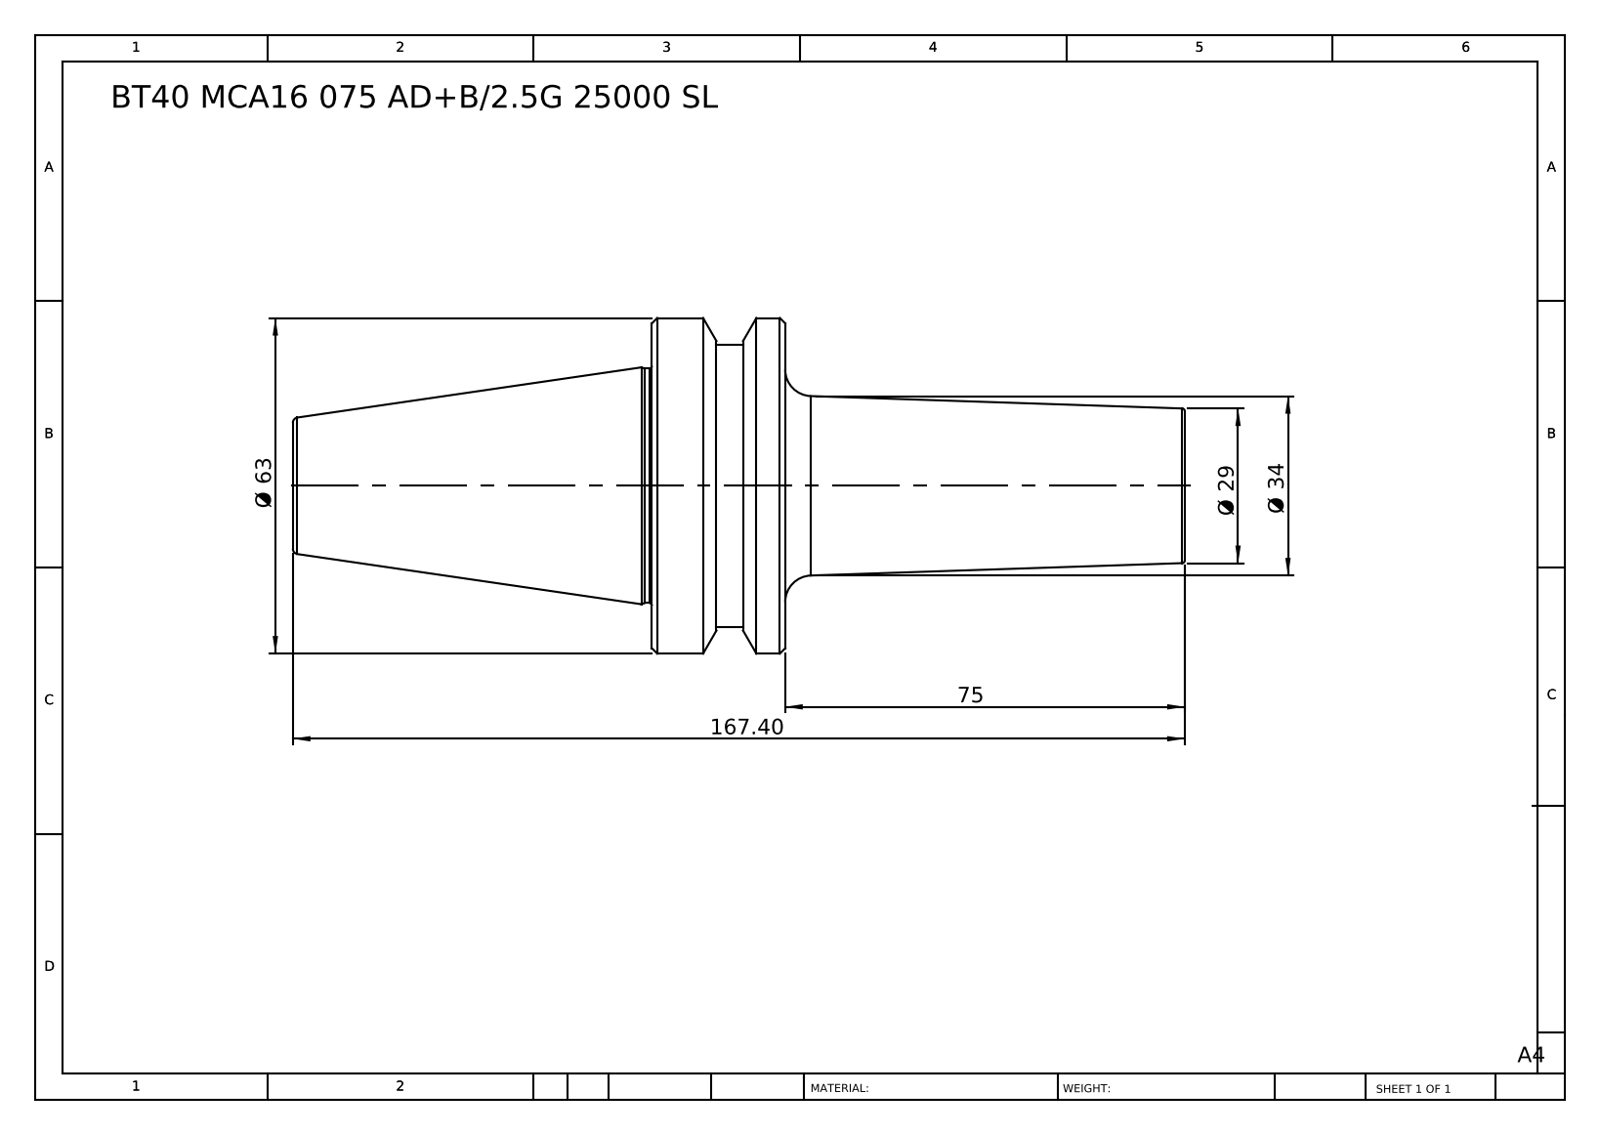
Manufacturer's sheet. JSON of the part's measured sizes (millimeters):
{"part_name": "BT40 MCA16 075 AD+B-2.5G 25000 SL", "step_written_by": "SolidWorks 2014 (CONFIG_CONTROL_DESIGN)", "units": "millimeters", "bodies": {"solids": 1, "faces": 38, "planar": 6, "cylindrical": 8, "other": 24}, "overall_size": [167.4, 63, 63], "volume_mm3": 197476, "surface_area_mm2": 25292, "round_bosses_or_shafts": [[63, 1], [53, 1], [44, 1]], "face_to_face_distances": [25, 75, 100, 167.4, 92.4, 67.4, 87.9, 12.9, 12.1, 79.5]}
